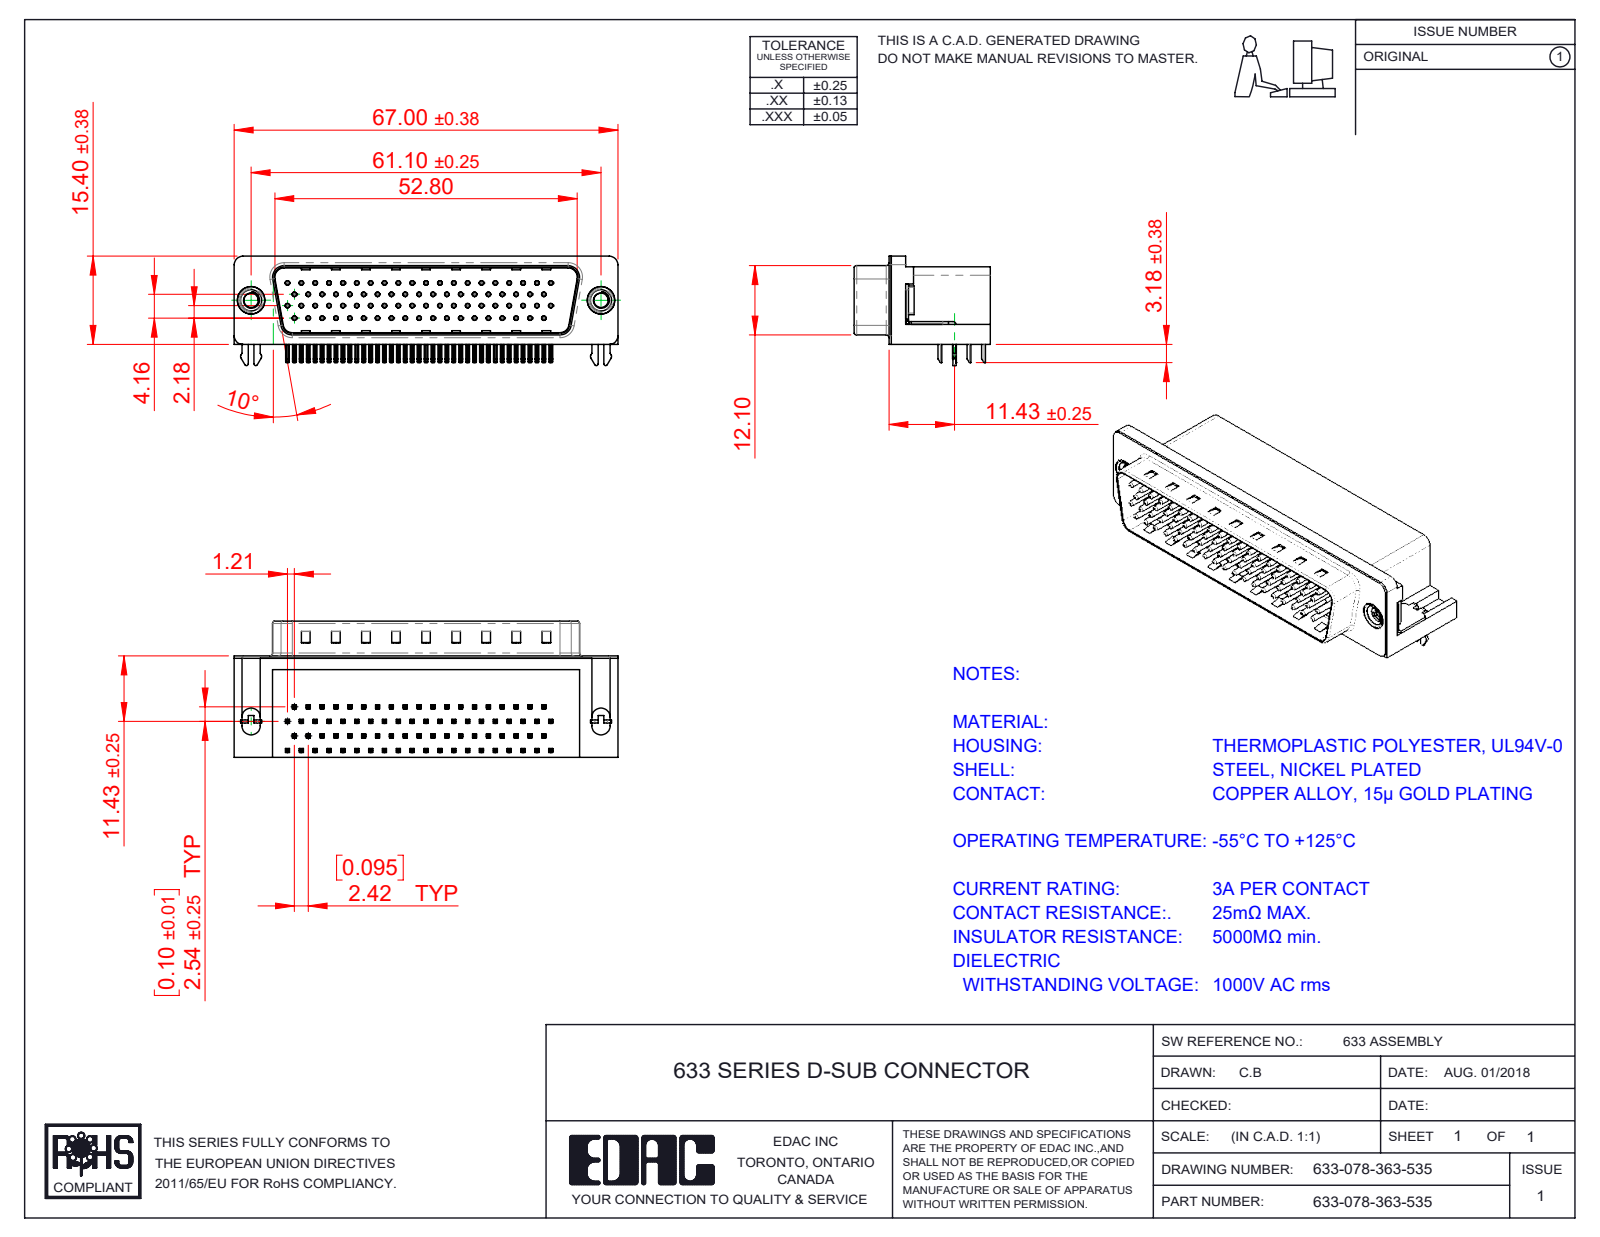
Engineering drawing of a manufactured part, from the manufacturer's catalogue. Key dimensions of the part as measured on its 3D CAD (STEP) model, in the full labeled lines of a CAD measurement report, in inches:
Part name (STEP PRODUCT): 633 Contact Top 78; 633 Contact Bottom_78 Contact; 633 Housing_78 Contact; 633-078-363-535 (+5 more)
STEP written by: SolidWorks 2016 (CONFIG_CONTROL_DESIGN)
Units: inches
Bodies: 84 solids, 6316 faces (4013 planar, 1790 cylindrical, 513 other)
Overall size (bounding box): 2.638 × 0.937 × 0.752
Volume: 0.891 in³ · Surface area: 25.36 in²
Round holes (diameter × count): ⌀0.014 ×78, ⌀0.031 ×78, ⌀0.098 ×2, ⌀0.157 ×2, ⌀0.189 ×2, ⌀0.197 ×2
Round bosses / shafts (diameter × count): ⌀0.03 ×78, ⌀0.193 ×2, ⌀0.187 ×2, ⌀0.154 ×2
Partial cylindrical surfaces — rounded edges, fillets, slot ends (radius × count): R0.01 ×320, R0.005 ×156, R0.039 ×16, R0.02 ×14, R0.063 ×8, R0.059 ×6, R0.013 ×4, R0.018 ×4
Main face-to-face distances: 0.016, 0.52, 0.681, 0.461, 0.526, 0.081, 0.541, 0.065, 0.073, 0.469
Hole centre spacings: 0.095, 0.191, 0.286, 0.381, 0.246, 0.281, 0.476, 0.339
